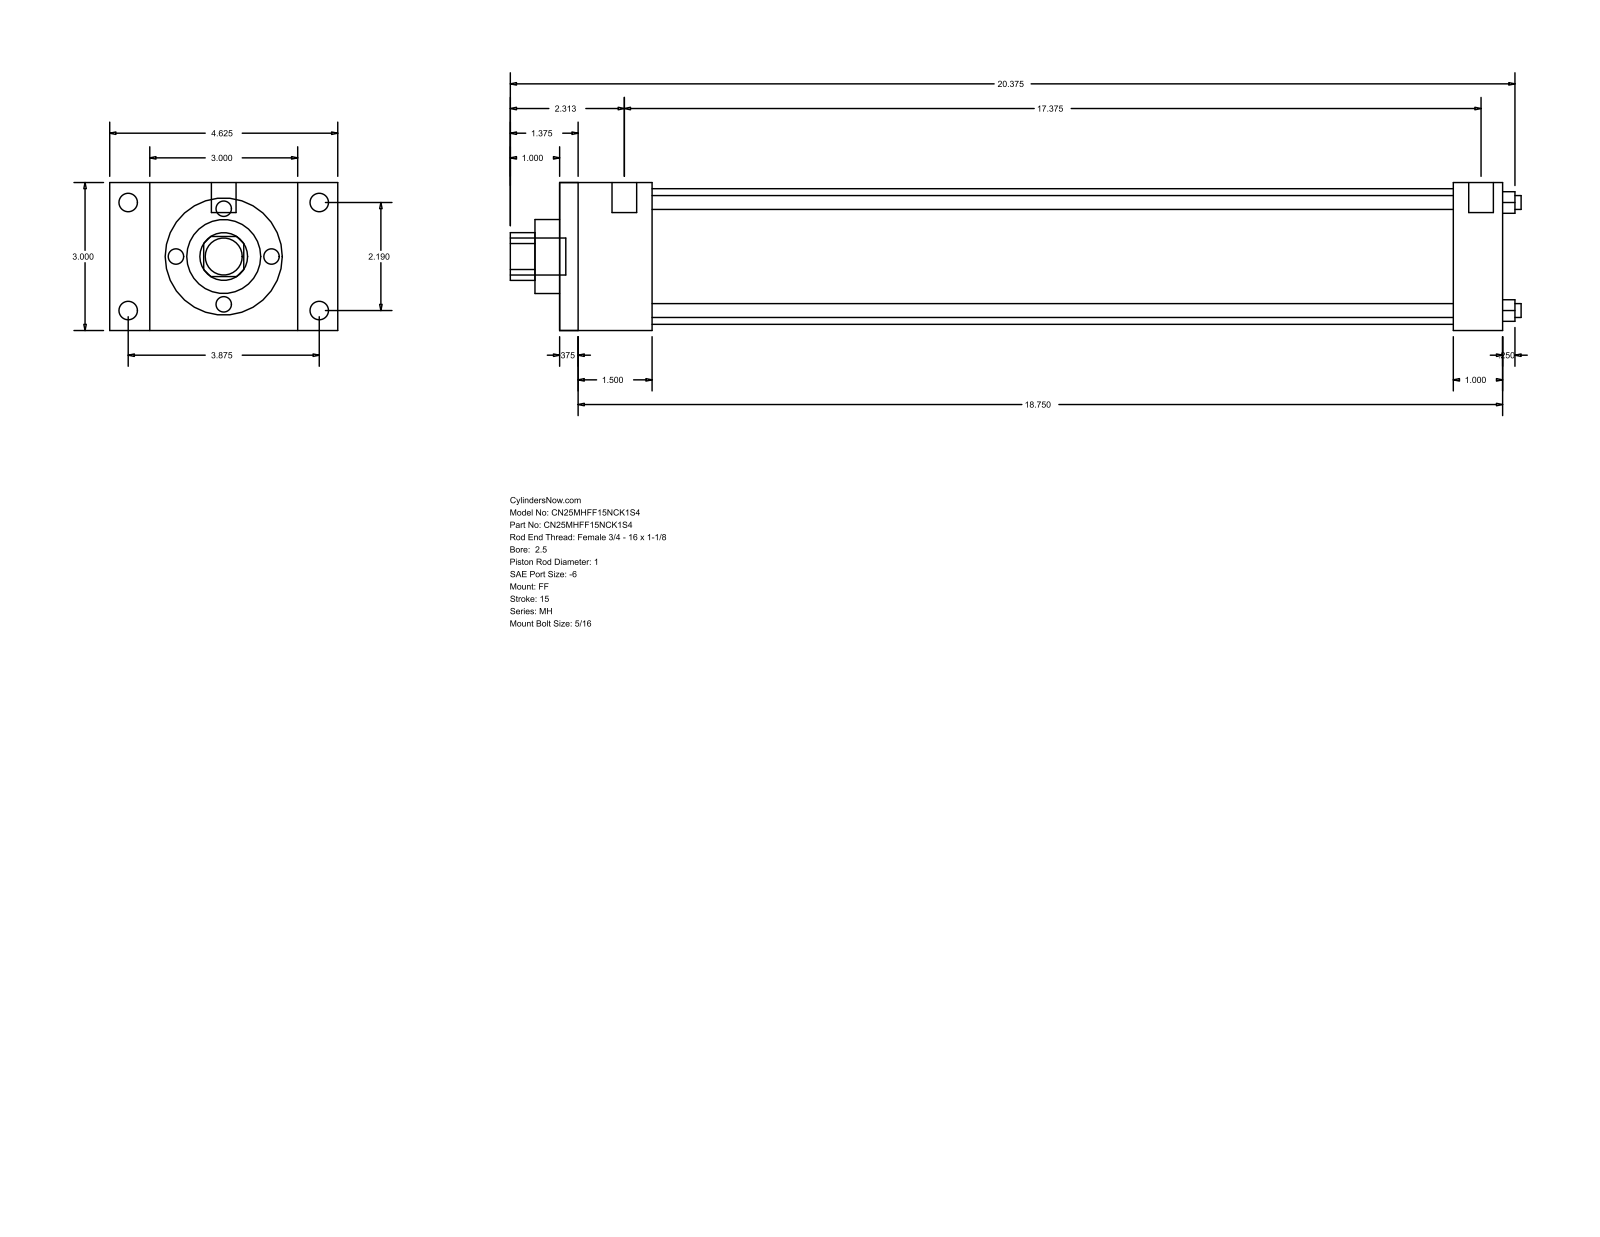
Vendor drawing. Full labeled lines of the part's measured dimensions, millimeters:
Part name (STEP PRODUCT): MH_FF__0250_1
STEP written by: GSSL Pune (CONFIG_CONTROL_DESIGN)
Units: millimetres
Bodies: 0 solids, 92 faces (64 planar, 28 cylindrical, 0 other)
Overall size (bounding box): 520.7 × 117.47 × 76.2
Round holes (diameter × count): ⌀7.14 ×4, ⌀25.4 ×1, ⌀38.1 ×1, ⌀69.85 ×1
Round bosses / shafts (diameter × count): ⌀9.53 ×4, ⌀5.56 ×4, ⌀12.7 ×2, ⌀19.05 ×1
Partial cylindrical surfaces — rounded edges, fillets, slot ends (radius × count): R12.29 ×1
Main face-to-face distances: 76.2, 485.78, 9.52, 476.26, 47.63, 460.37, 38.11, 450.85, 412.74, 438.15
Hole centre spacings: 39.33, 55.62, 78.66
